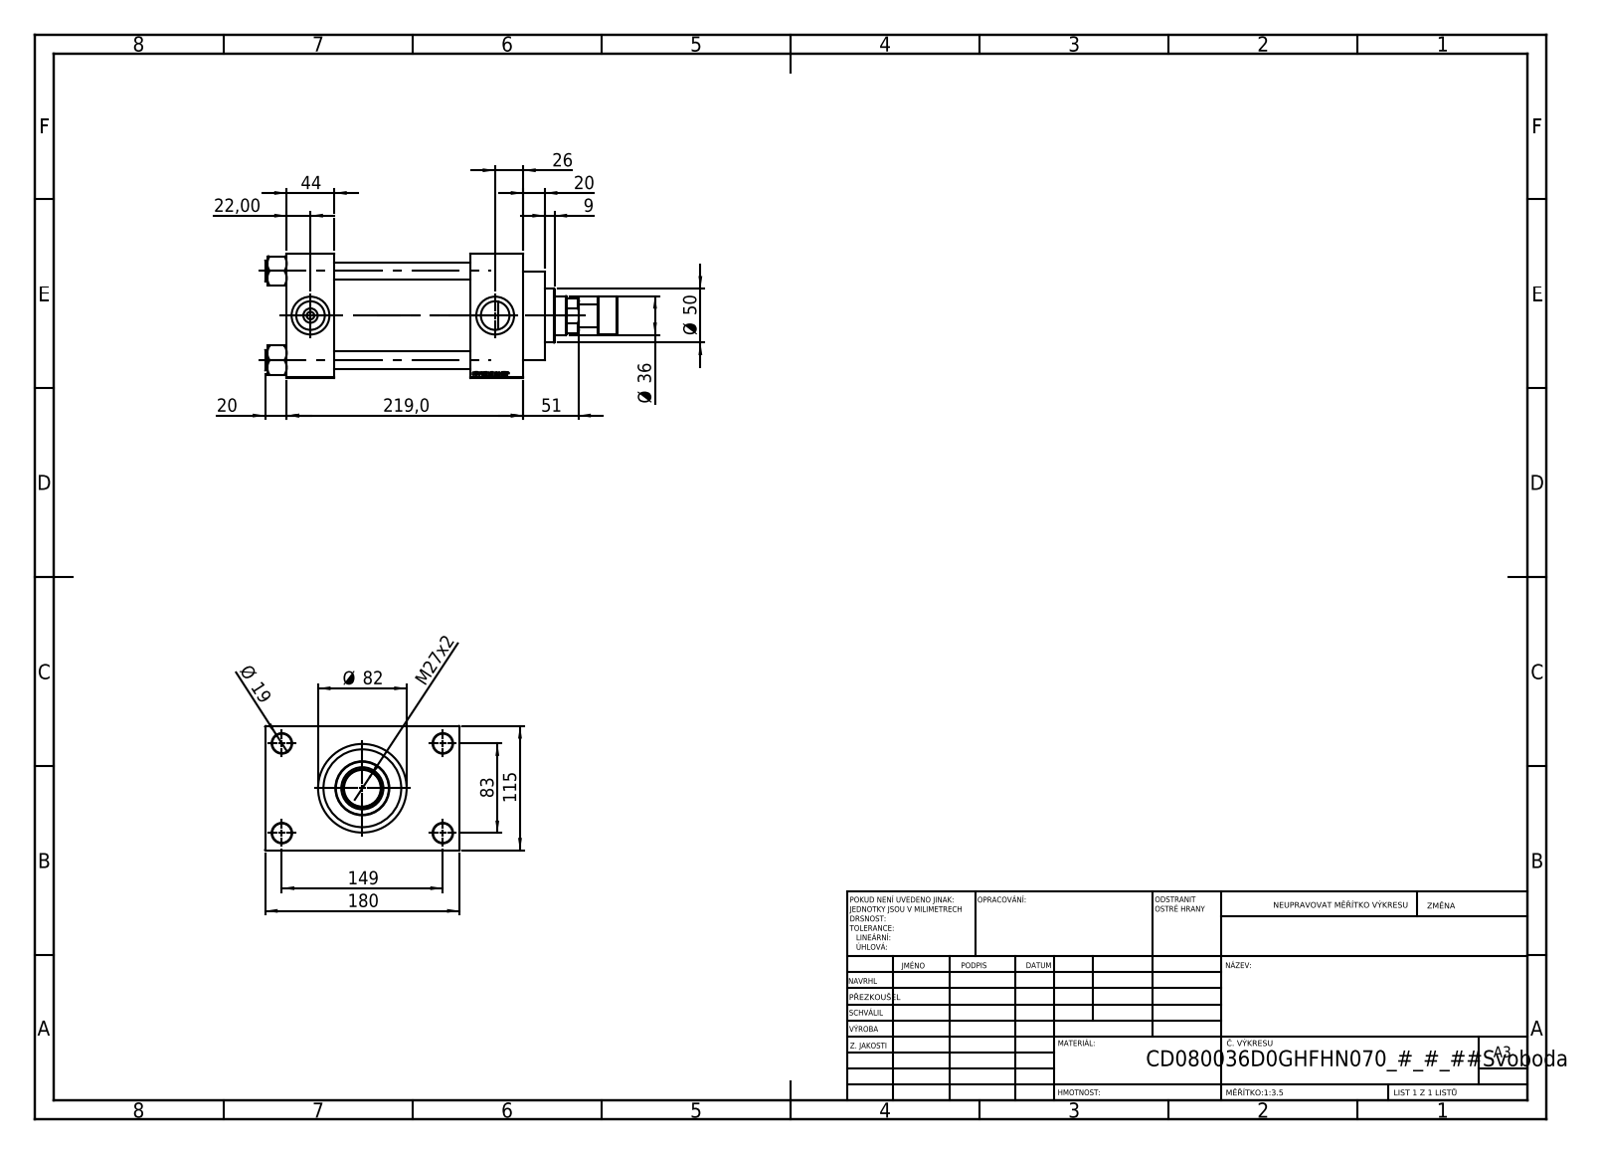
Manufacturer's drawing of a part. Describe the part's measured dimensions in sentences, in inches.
The part is named "V215CD_NUT_M5_D; V215CR_ROD_END_F; V215CD_D_Body; V215CD_VCP_D (+2 more)". Its 3-D file was written by "SolidWorks 2019 (CONFIG_CONTROL_DESIGN)". It is 12 solids with 1165 faces: 549 planar, 92 cylindrical and 524 other. Overall it measures 12.835 by 7.087 by 4.528 inches. Its volume is 131.8 cubic inches and its surface area 546.1 square inches. Round holes: 4 of diameter 0.63, 4 of diameter 0.709, 2 of diameter 0.276, 2 of diameter 1.041, 2 of diameter 1.378, 1 of diameter 1.004, 1 of diameter 1.417, 1 of diameter 1.535, 1 of diameter 2.402, 1 of diameter 2.835, 1 of diameter 3.15. Round bosses or shafts: 4 of diameter 0.748, 1 of diameter 3.386, 1 of diameter 3.228, 1 of diameter 1.969, 1 of diameter 1.378, 1 of diameter 0.827. The main face-to-face distances are 4.528, 4.961, 1.929, 6.89, 6.693, 1.732, 8.622, 1.28, 5.807, 7.087. The hole center spacings are 1.305, 2.302, 3.256, 3.357, 3.513, 4.561, 5.607, 3.268.
